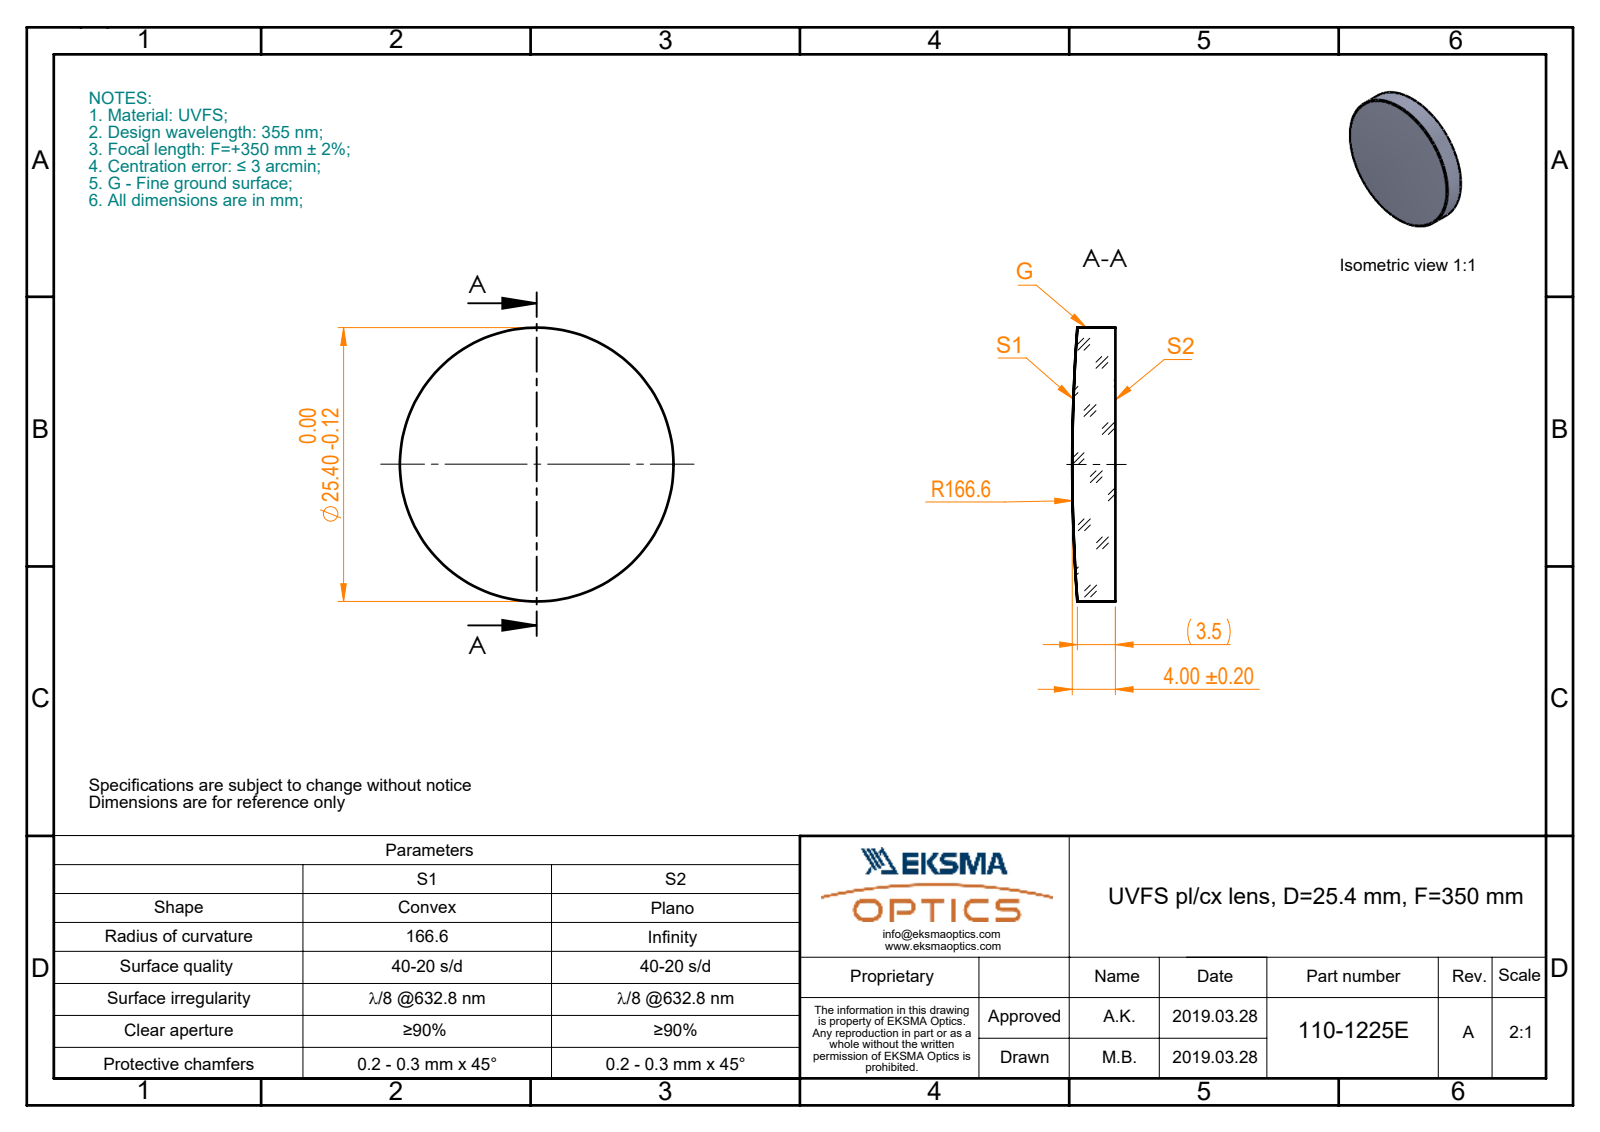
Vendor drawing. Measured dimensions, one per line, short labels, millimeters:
name: 110-1225E UVFS pl-cx 25.4 F350
written by: SolidWorks 2017 (CONFIG_CONTROL_DESIGN)
unit: mm
bodies: 1 solid, 5 faces (1 planar, 2 cylindrical, 2 other)
size: 25.4 × 25.4 × 4
volume: 1 904 mm³; area: 1 295 mm²
bosses: 1× ⌀25.4
